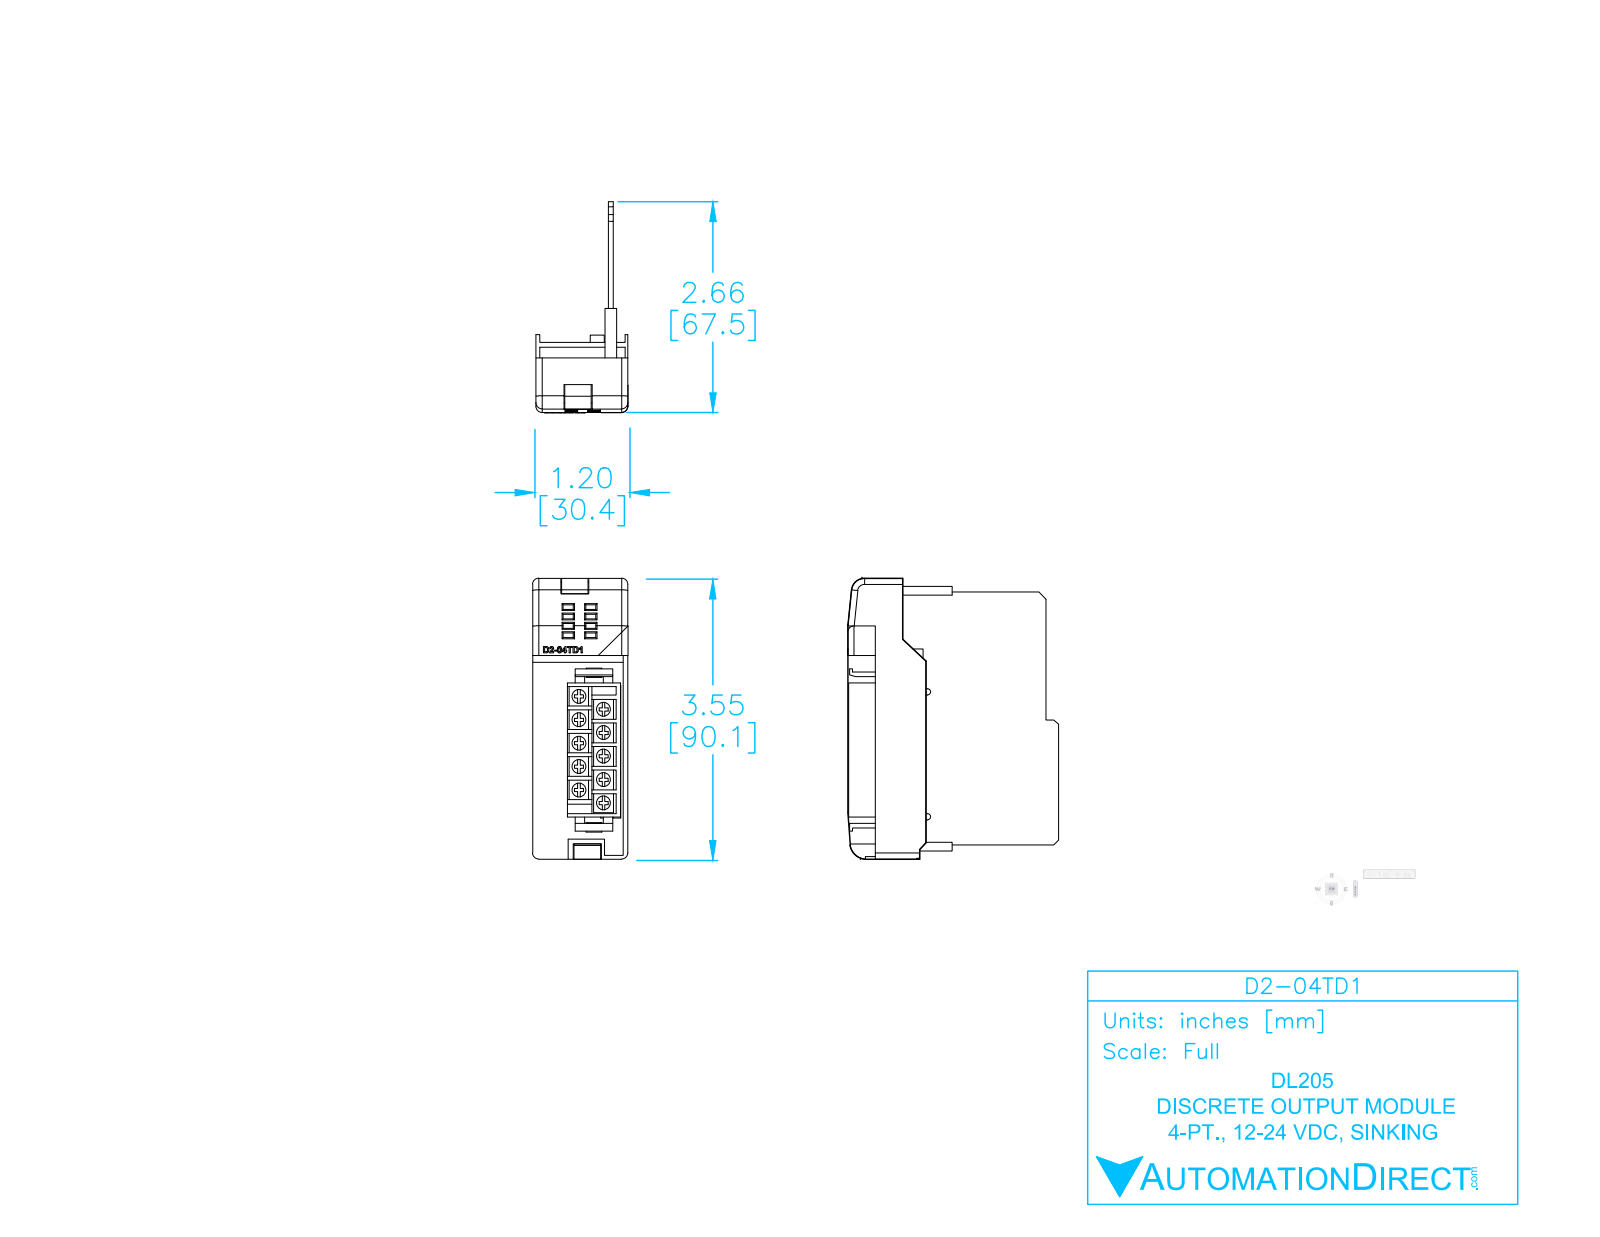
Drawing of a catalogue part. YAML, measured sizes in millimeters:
part_name: "D2-04TD1_ModuleCase_light_NEW"
step_written_by: "SolidWorks 2009 (AUTOMOTIVE_DESIGN)"
units: millimeters
bodies: {solids: 4, faces: 586, planar: 423, cylindrical: 77, other: 86}
overall_size: [90, 67.14, 30.55]
volume: 25603
surface_area: 28826
round_bosses_or_shafts:
  - {diameter: 4.5, count: 10}
partial_cylinders:
  - {radius: 0.35, count: 16}
  - {radius: 2, count: 9}
  - {radius: 0.25, count: 4}
  - {radius: 1, count: 2}
  - {radius: 1.25, count: 2}
  - {radius: 4.12, count: 1}
  - {radius: 5.39, count: 1}
face_to_face_distances: [1.5, 4.72, 2.36, 6.22, 3.86, 0.86, 3.22, 30.5, 3.85, 8.14]
